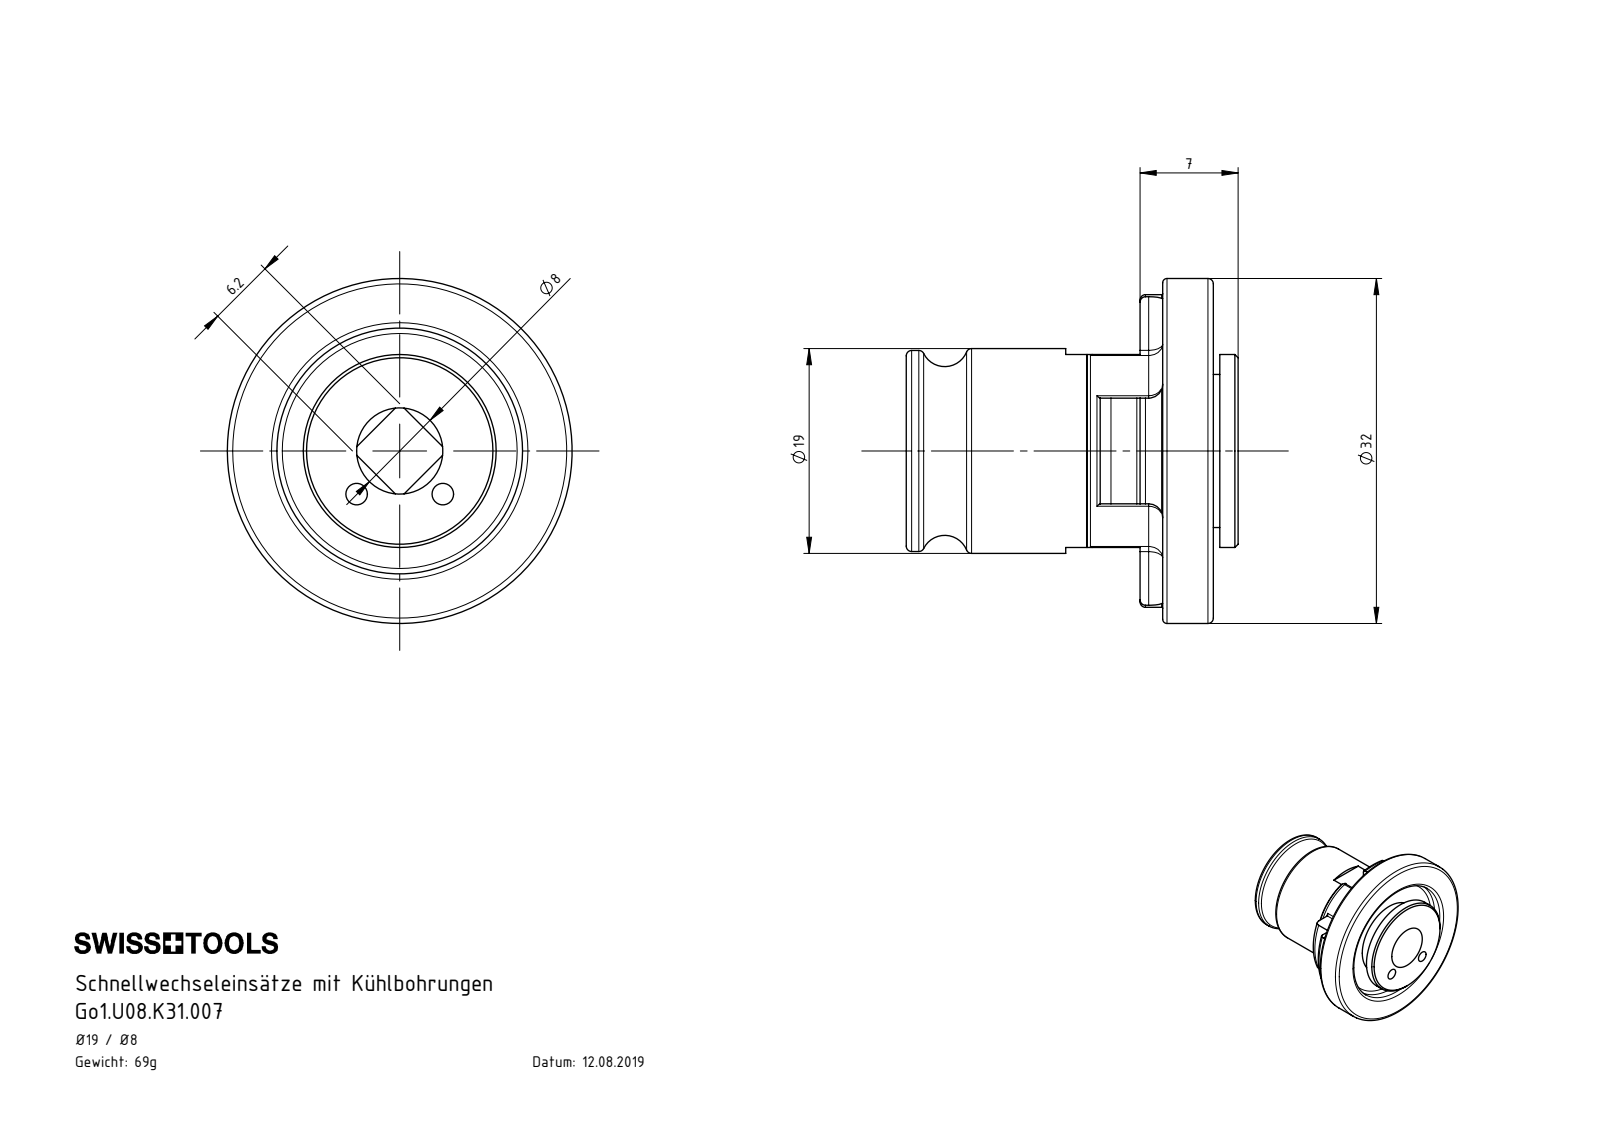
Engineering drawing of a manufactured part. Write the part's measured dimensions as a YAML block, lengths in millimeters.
part_name: "Go1.U08.K31.007"
step_written_by: "SolidWorks 2017 (AUTOMOTIVE_DESIGN)"
units: millimeters
bodies: {solids: 1, faces: 114, planar: 36, cylindrical: 34, other: 44}
overall_size: [32, 32, 30.8]
volume: 8771
surface_area: 5076
round_holes:
  - {diameter: 2, count: 2}
  - {diameter: 8, count: 1}
  - {diameter: 11.4, count: 1}
  - {diameter: 22.8, count: 1}
round_bosses_or_shafts:
  - {diameter: 32, count: 1}
  - {diameter: 19, count: 1}
  - {diameter: 18.65, count: 1}
  - {diameter: 18.52, count: 1}
  - {diameter: 17.9, count: 1}
  - {diameter: 14.2, count: 1}
partial_cylinders:
  - {radius: 0.5, count: 8}
  - {radius: 1.3, count: 4}
  - {radius: 12.4, count: 1}
  - {radius: 14.5, count: 1}
face_to_face_distances: [2.35, 4.7, 7, 4.65, 2.3, 23.8, 26.15, 28.5, 30.8, 29.1]
hole_center_spacings: [5.66, 8]
